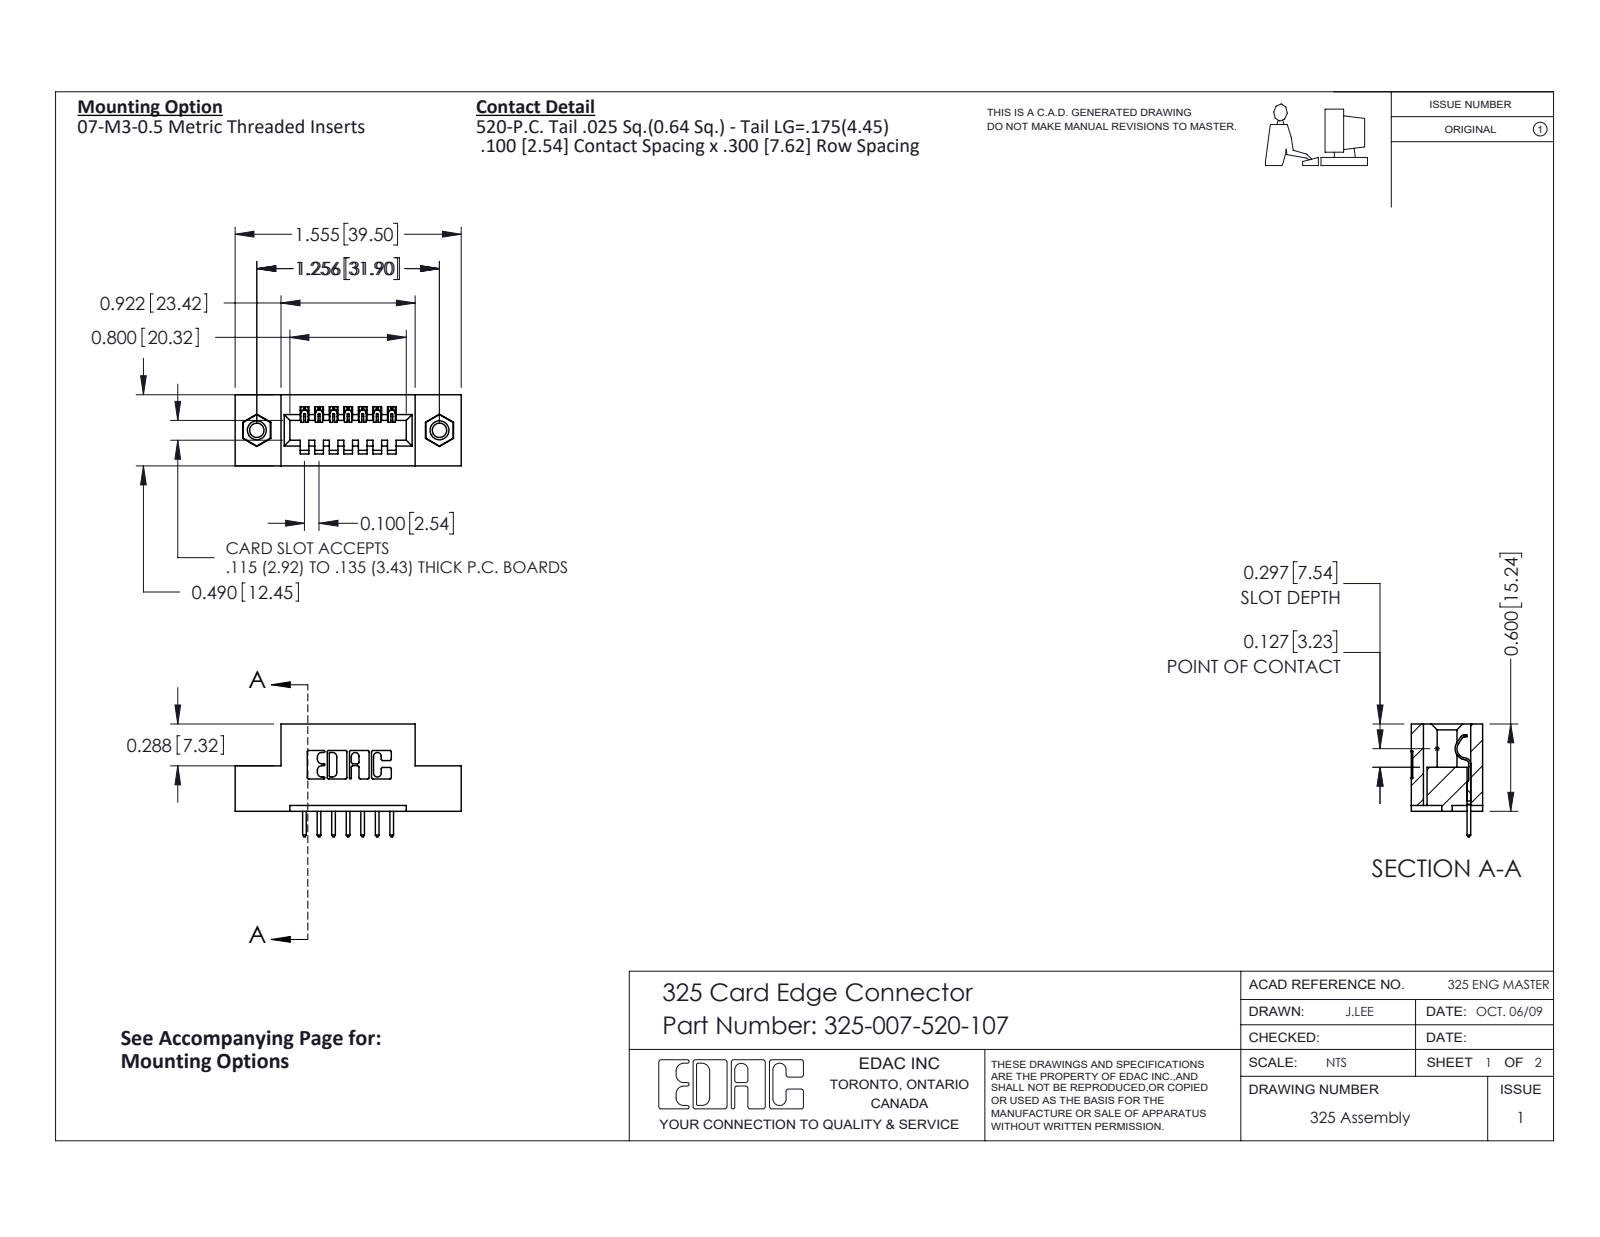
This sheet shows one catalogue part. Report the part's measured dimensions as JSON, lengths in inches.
{"part_name": "325-007-520-107; 325 Part_TI; 325-292-001_325-293-120; 345-250-001_345-250-005-103", "step_written_by": "SolidWorks 2016 (CONFIG_CONTROL_DESIGN)", "units": "inches", "bodies": {"solids": 10, "faces": 580, "planar": 396, "cylindrical": 168, "other": 16}, "overall_size": [1.555, 0.775, 0.49], "volume_in3": 0.287, "surface_area_in2": 6.979, "round_holes": [[0.098, 2], [0.125, 2], [0.16, 2]], "round_bosses_or_shafts": [[0.155, 2]], "partial_cylinders_radius": [[0.01, 22], [0.006, 14], [0.01, 14], [0.007, 6], [0.031, 6], [0.026, 3], [0.014, 1], [0.022, 1]], "face_to_face_distances": [0.3, 0.1, 0.2, 0.04, 0.49, 0.083, 0.407, 0.06, 0.16, 0.4], "hole_center_spacings": [1.256]}
